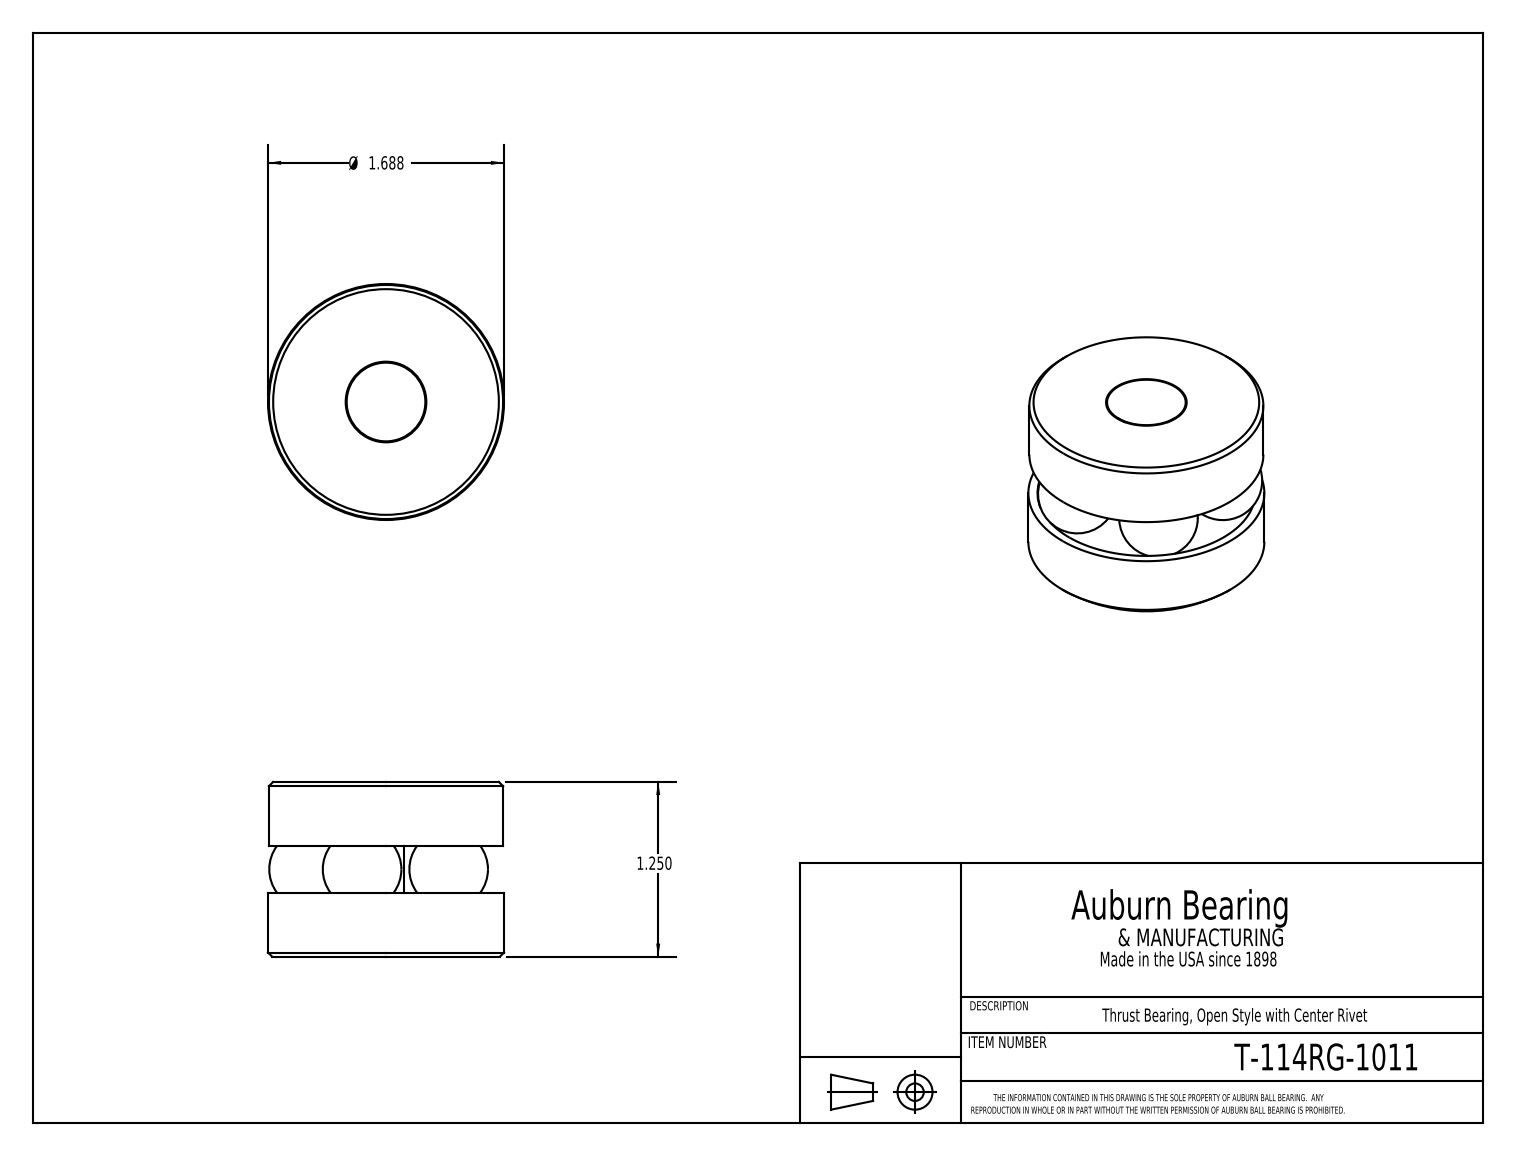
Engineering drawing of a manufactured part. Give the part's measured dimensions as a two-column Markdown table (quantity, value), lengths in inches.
| quantity | value |
| --- | --- |
| part name | T-114RG_T-114RG-1011 |
| STEP written by | SolidWorks 2016 (CONFIG_CONTROL_DESIGN) |
| units | inches |
| bodies | 8 solids, 26 faces (8 planar, 5 cylindrical, 13 other) |
| overall size | 1.688 × 1.688 × 1.25 |
| volume | 2.25 in³ |
| surface area | 21.21 in² |
| round holes (diameter × count) | 0.26 × 1 |
| round bosses / shafts (diameter × count) | 1.687 × 1, 1.673 × 1, 0.25 × 1 |
| main face-to-face distances | 1.25, 0.456, 0.794, 0.337 |
